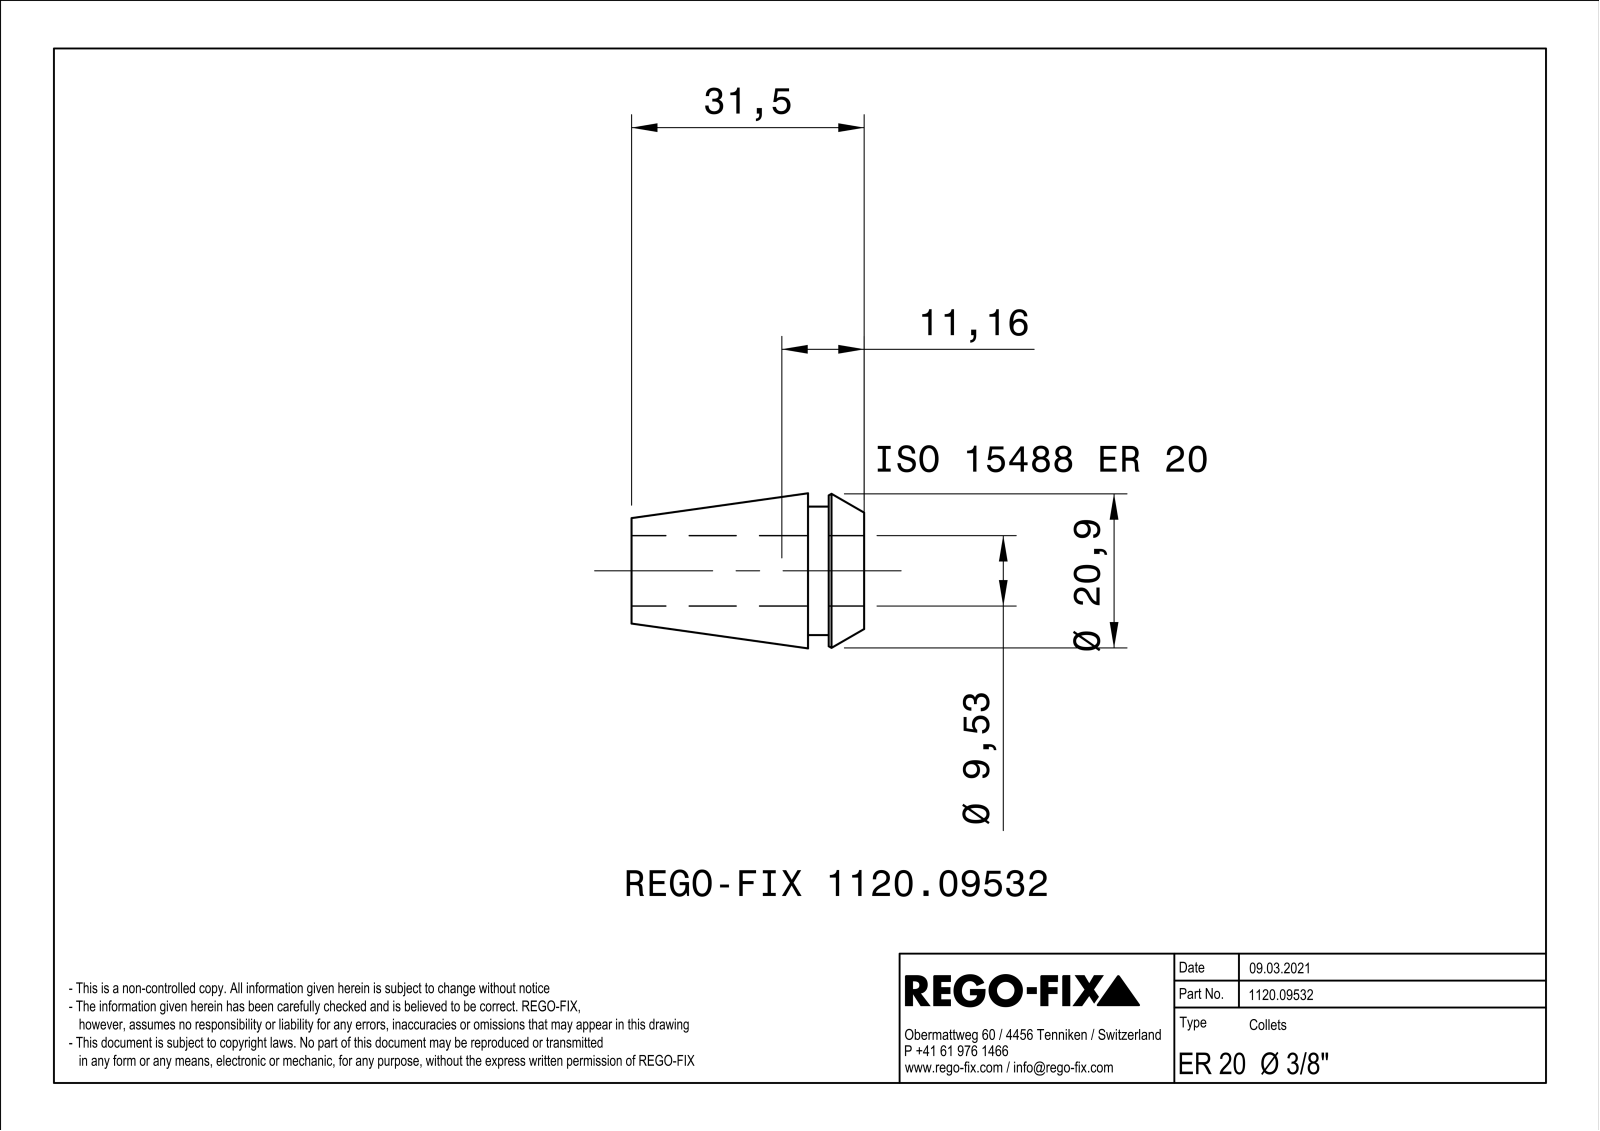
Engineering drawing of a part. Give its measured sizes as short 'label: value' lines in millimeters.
name: NOCUT
written by: SIEMENS PLM Software Solid Edge ST10 (AUTOMOTIVE_DESIGN)
unit: mm
bodies: 1 solid, 177 faces (88 planar, 9 cylindrical, 80 other)
size: 31.5 × 20.99 × 20.99
volume: 4 535 mm³; area: 6 254 mm²
holes: 1× ⌀9.53
bosses: 1× ⌀17.4
face distances: 0.6, 7.6, 4.8, 2.8, 31.5, 26.7, 23.9, 5.5, 0.7, 2.1
